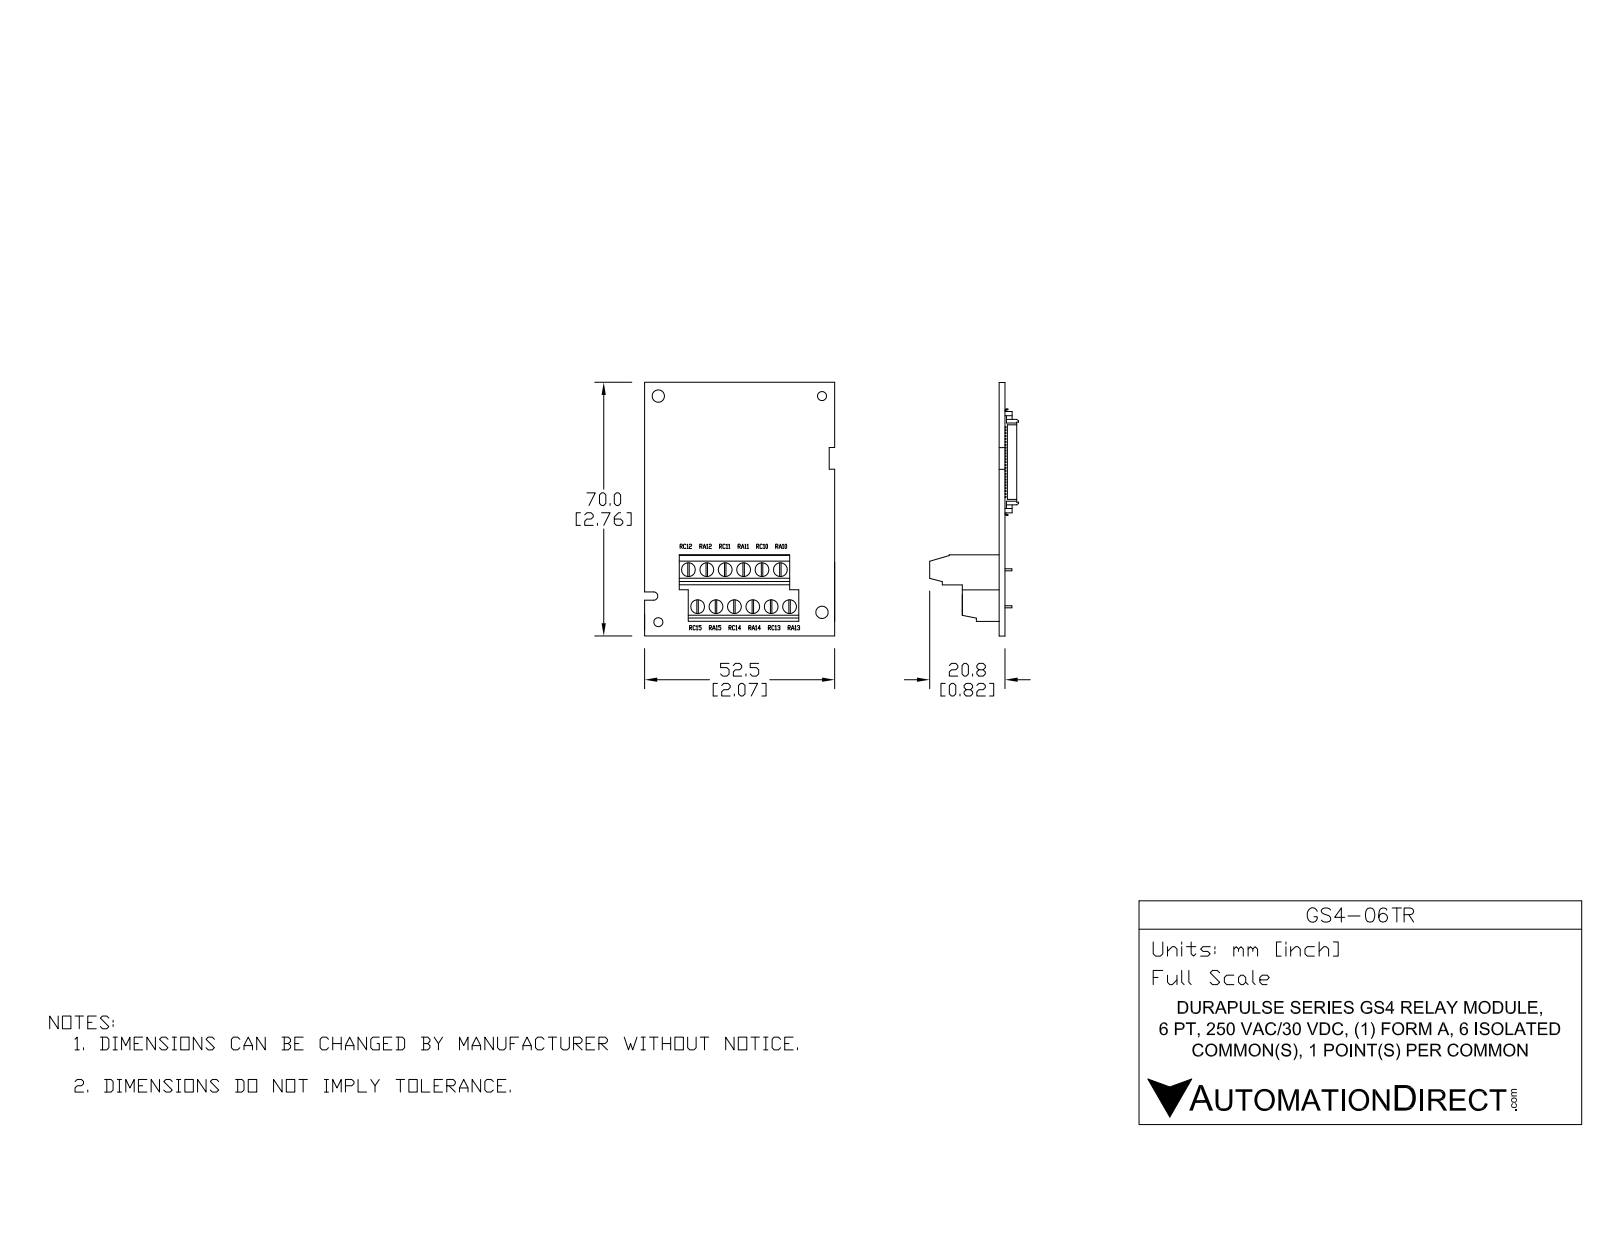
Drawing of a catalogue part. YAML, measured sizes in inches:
part_name: "GS4-06TR"
step_written_by: "SolidWorks 2016 (AUTOMOTIVE_DESIGN)"
units: inches
bodies: {solids: 3, faces: 743, planar: 670, cylindrical: 69, other: 4}
overall_size: [2.756, 2.067, 0.967]
volume: 0.745
surface_area: 19.42
round_holes:
  - {diameter: 0.15, count: 12}
  - {diameter: 0.039, count: 9}
  - {diameter: 0.098, count: 2}
  - {diameter: 0.134, count: 2}
  - {diameter: 0.031, count: 1}
partial_cylinders:
  - {radius: 0.01, count: 4}
  - {radius: 0.02, count: 4}
  - {radius: 0.045, count: 1}
face_to_face_distances: [0.063, 0.15, 1.202, 0.118, 0.098, 0.397, 0.465, 0.402, 0.02, 0.354]
hole_center_spacings: [0.414, 0.2, 0.501, 0.4, 0.641, 0.6, 0.807, 0.1]
